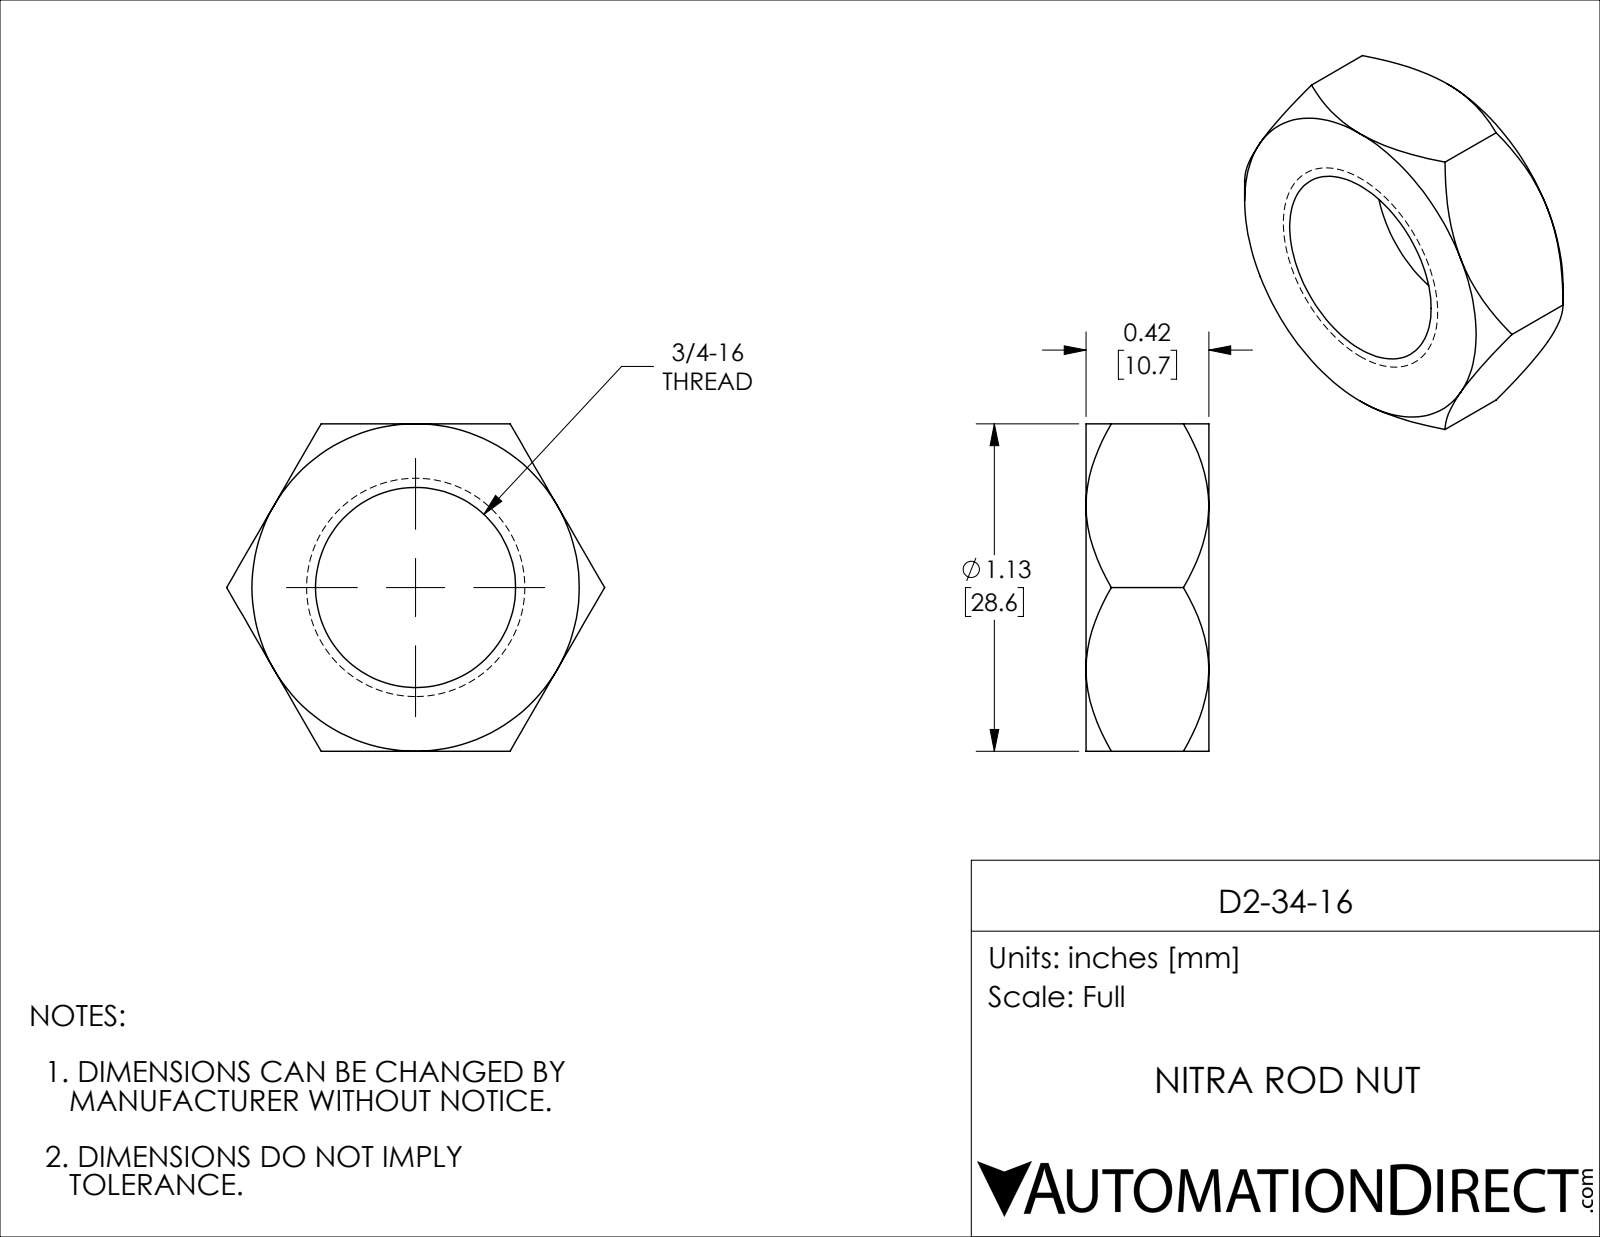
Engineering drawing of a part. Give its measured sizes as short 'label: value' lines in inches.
name: D2-34-16
written by: SolidWorks 2019 (CONFIG_CONTROL_DESIGN)
unit: in
bodies: 1 solid, 24 faces (8 planar, 2 cylindrical, 14 other)
size: 1.299 × 1.125 × 0.422
volume: 0.301 in³; area: 3.858 in²
holes: 1× ⌀0.687
face distances: 1.125, 0.422
